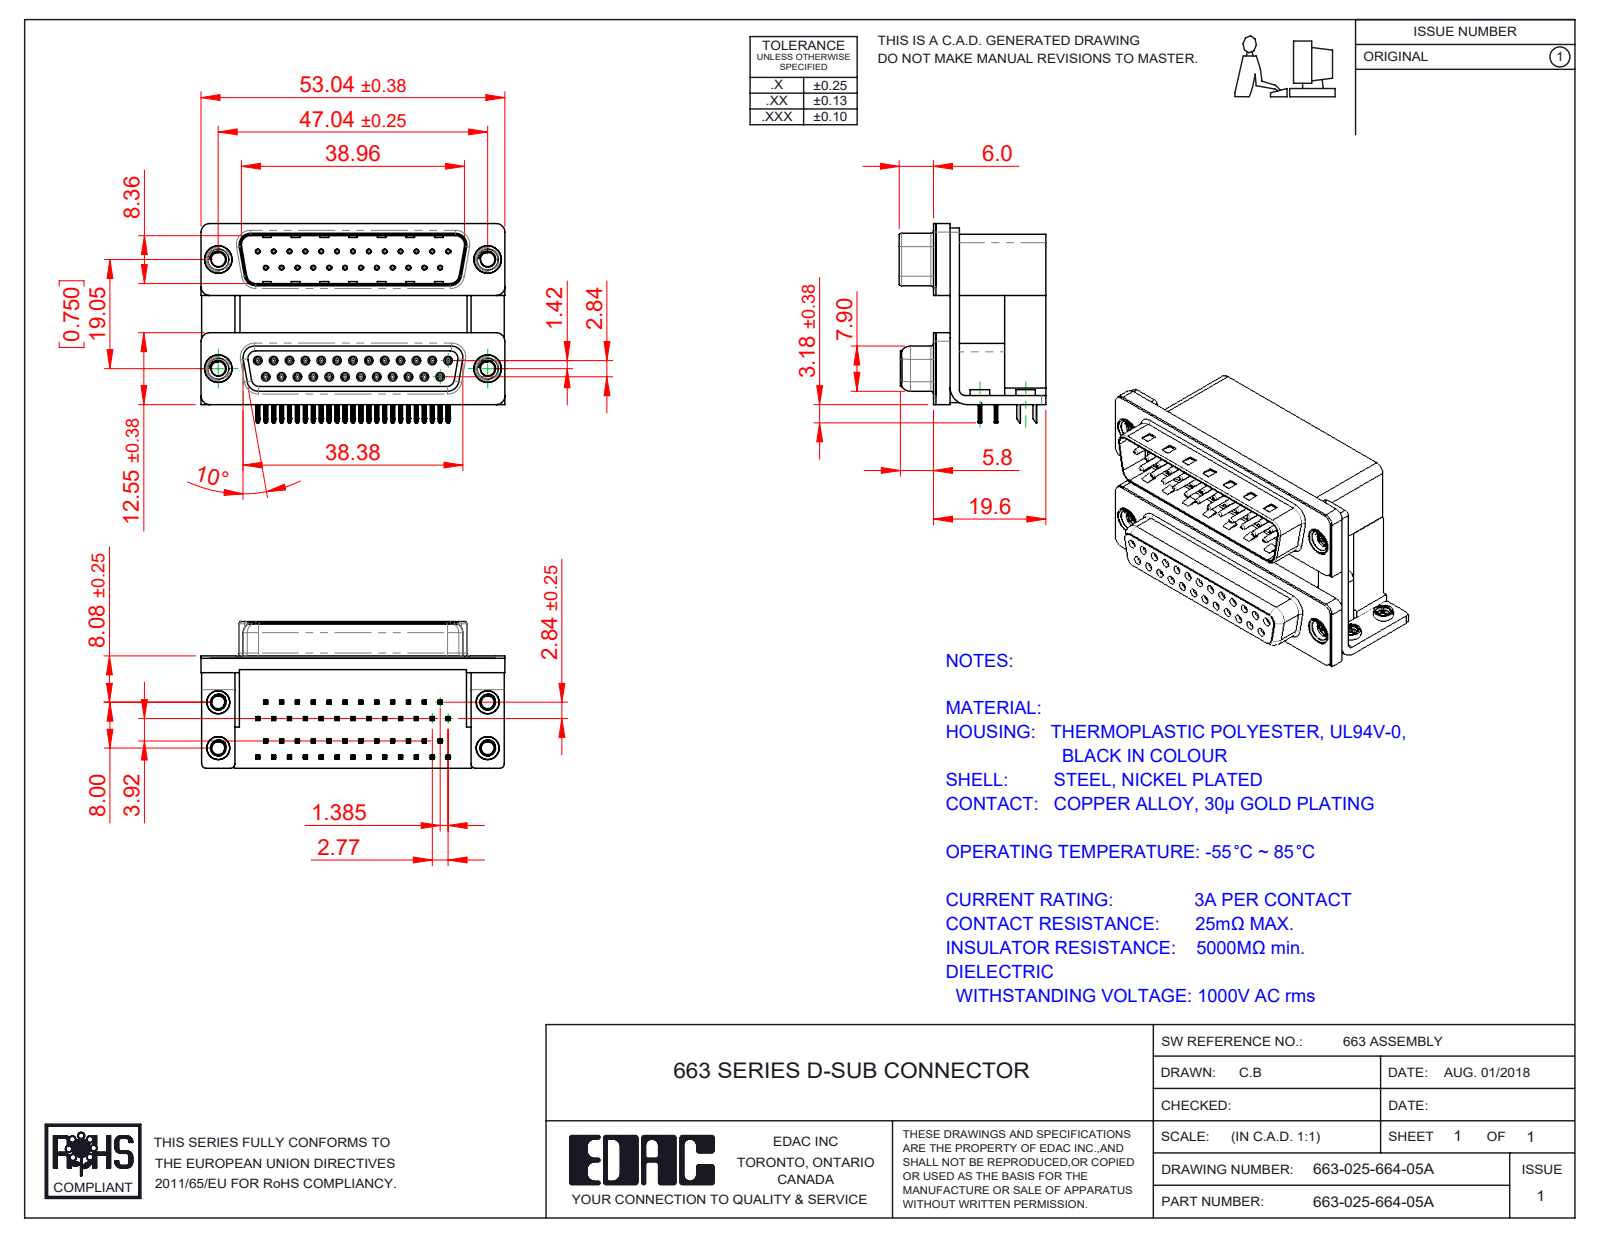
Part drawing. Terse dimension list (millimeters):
name: 663 Housing Spacer_25 Contacts M; 663 Mounting Bracket_ThruM; 663-025-664-05A; 663 Contact Top Upper_M (+8 more)
written by: SolidWorks 2020 (CONFIG_CONTROL_DESIGN)
unit: mm
bodies: 65 solids, 6347 faces (3269 planar, 1627 cylindrical, 1451 other)
size: 53.04 × 34.78 × 25.6
volume: 22 599 mm³; area: 24 154 mm²
holes: 50× ⌀0.8, 25× ⌀0.35, 25× ⌀0.9, 4× ⌀2.26, 4× ⌀2.5, 4× ⌀2.75, 4× ⌀3.2, 4× ⌀3.5, 4× ⌀4, 4× ⌀4.8, 4× ⌀5
bosses: 25× ⌀1.2, 25× ⌀0.75, 4× ⌀4.9, 4× ⌀4.75, 4× ⌀4, 4× ⌀3.9, 4× ⌀3.4
rounds: 200× R0.1, 100× R0.15, 100× R0.25, 50× R0.12, 50× R0.35, 25× R0.34, 14× R1.5, 12× R0.28
face distances: 19.2, 0.4, 7.2, 12, 10.69, 16.7, 9.5, 2.5, 18.71, 29.4
hole spacings: 3.16, 2.77, 5.54, 11.08, 8.31, 5.03, 13.85, 7.48
